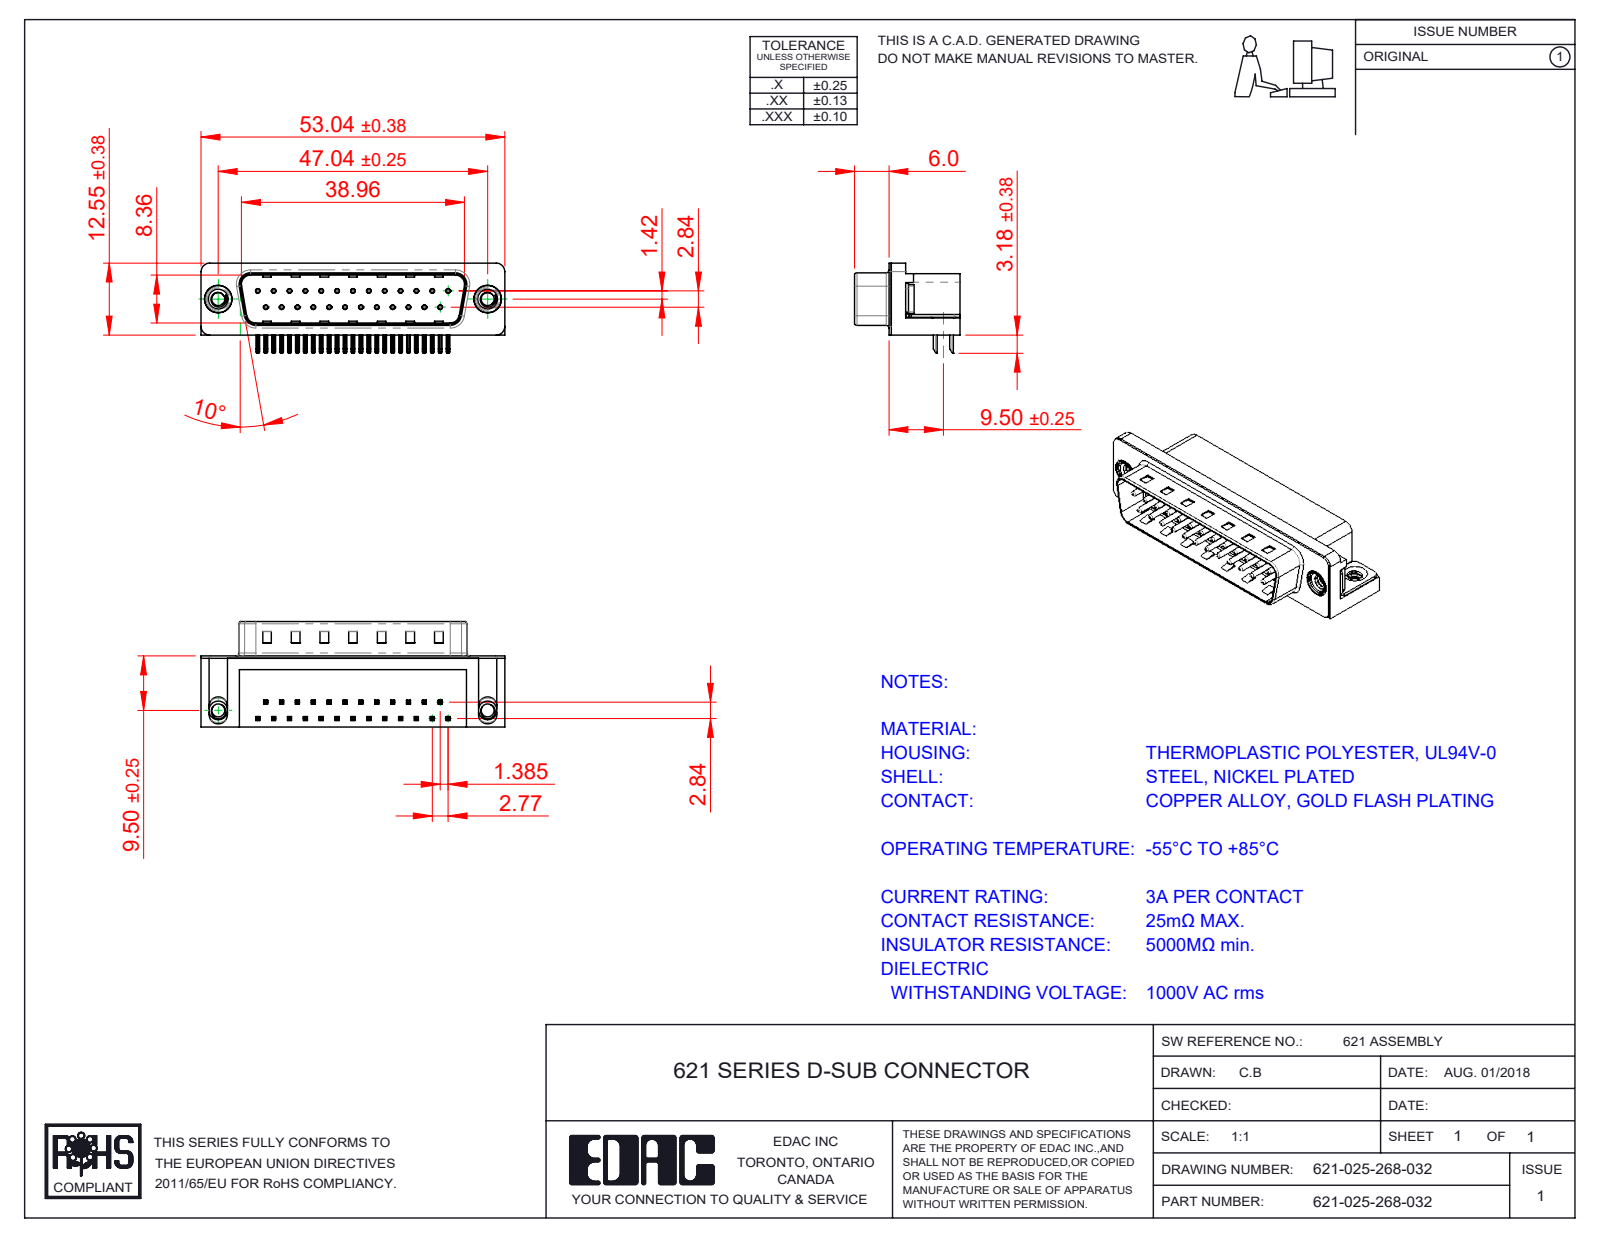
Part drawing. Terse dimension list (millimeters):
name: 621 Shell_25 Socket; 621 Housing_25 Socket; 621 Contact Top; 621 4-40 Threaded Rivet (+3 more)
written by: SolidWorks 2016 (CONFIG_CONTROL_DESIGN)
unit: mm
bodies: 31 solids, 2303 faces (1437 planar, 667 cylindrical, 199 other)
size: 53.04 × 18.4 × 16.25
volume: 6 348 mm³; area: 7 689 mm²
holes: 25× ⌀0.35, 25× ⌀0.8, 2× ⌀2.26, 2× ⌀4, 2× ⌀4.8, 2× ⌀5
bosses: 25× ⌀0.75, 2× ⌀4.9, 2× ⌀4.75, 2× ⌀3.9
rounds: 108× R0.25, 50× R0.12, 16× R1, 14× R0.5, 8× R1.6, 7× R1.5, 4× R0.32, 4× R0.9
face distances: 0.4, 12, 10.35, 2.1, 8.76, 10.46, 10.86, 1.7, 12.4, 9
hole spacings: 3.16, 2.77, 5.54, 8.31, 11.08, 13.85, 16.62, 5.03
